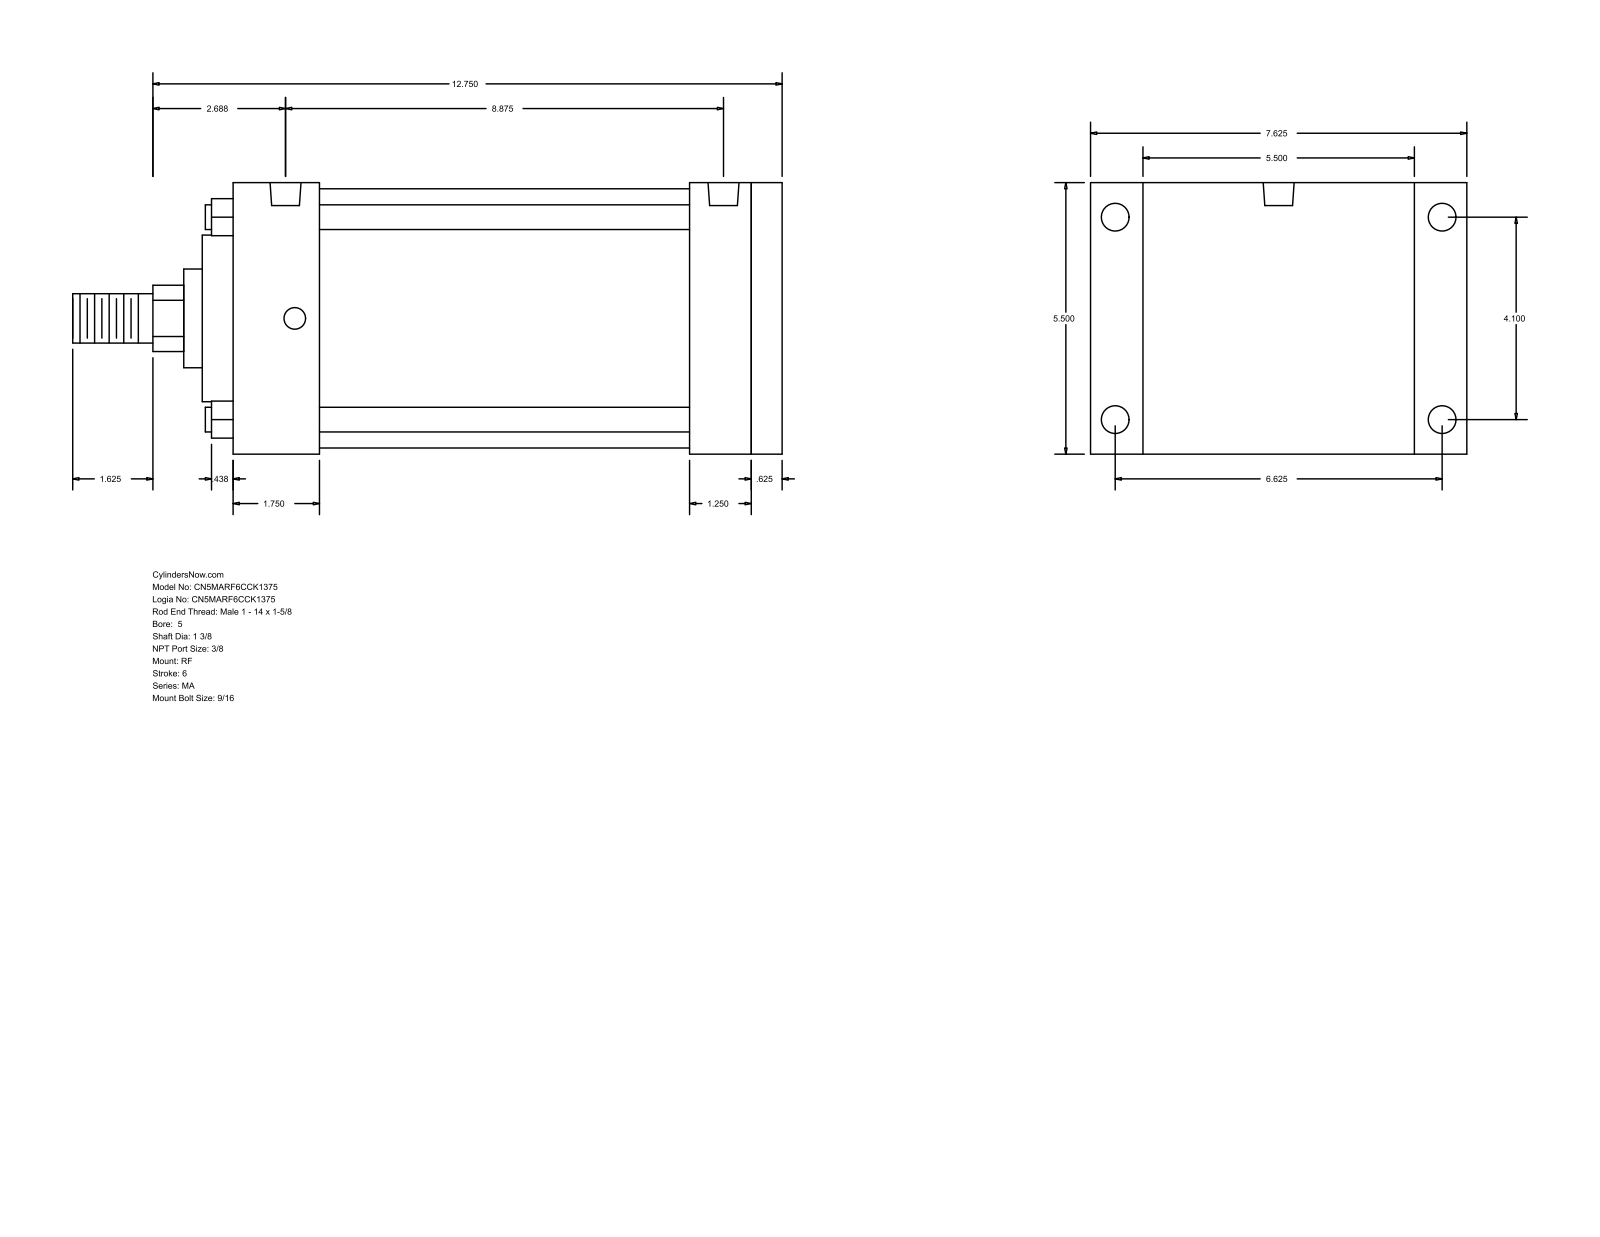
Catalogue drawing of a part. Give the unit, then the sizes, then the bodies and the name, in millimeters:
Units: millimetres
Overall size (bounding box): 365.12 × 193.68 × 139.7
Round holes (diameter × count): ⌀11.11 ×4, ⌀14.29 ×4, ⌀15.93 ×2
Round bosses / shafts (diameter × count): ⌀12.7 ×4, ⌀133.35 ×1, ⌀85.72 ×1, ⌀50.8 ×1, ⌀34.92 ×1, ⌀25.4 ×1
Partial cylindrical surfaces — rounded edges, fillets, slot ends (radius × count): R17.06 ×1
Main face-to-face distances: 139.7, 282.58, 15.87, 266.71, 44.45, 222.26, 238.13, 234.96, 190.51, 31.75
Hole centre spacings: 104.14, 168.28, 197.9, 215.9, 4.76, 4.77, 220.66, 220.67
Bodies: 0 solids, 94 faces (65 planar, 29 cylindrical, 0 other)
Part name (STEP PRODUCT): MA_RF__0500_1.375
STEP written by: GSSL Pune (CONFIG_CONTROL_DESIGN)
